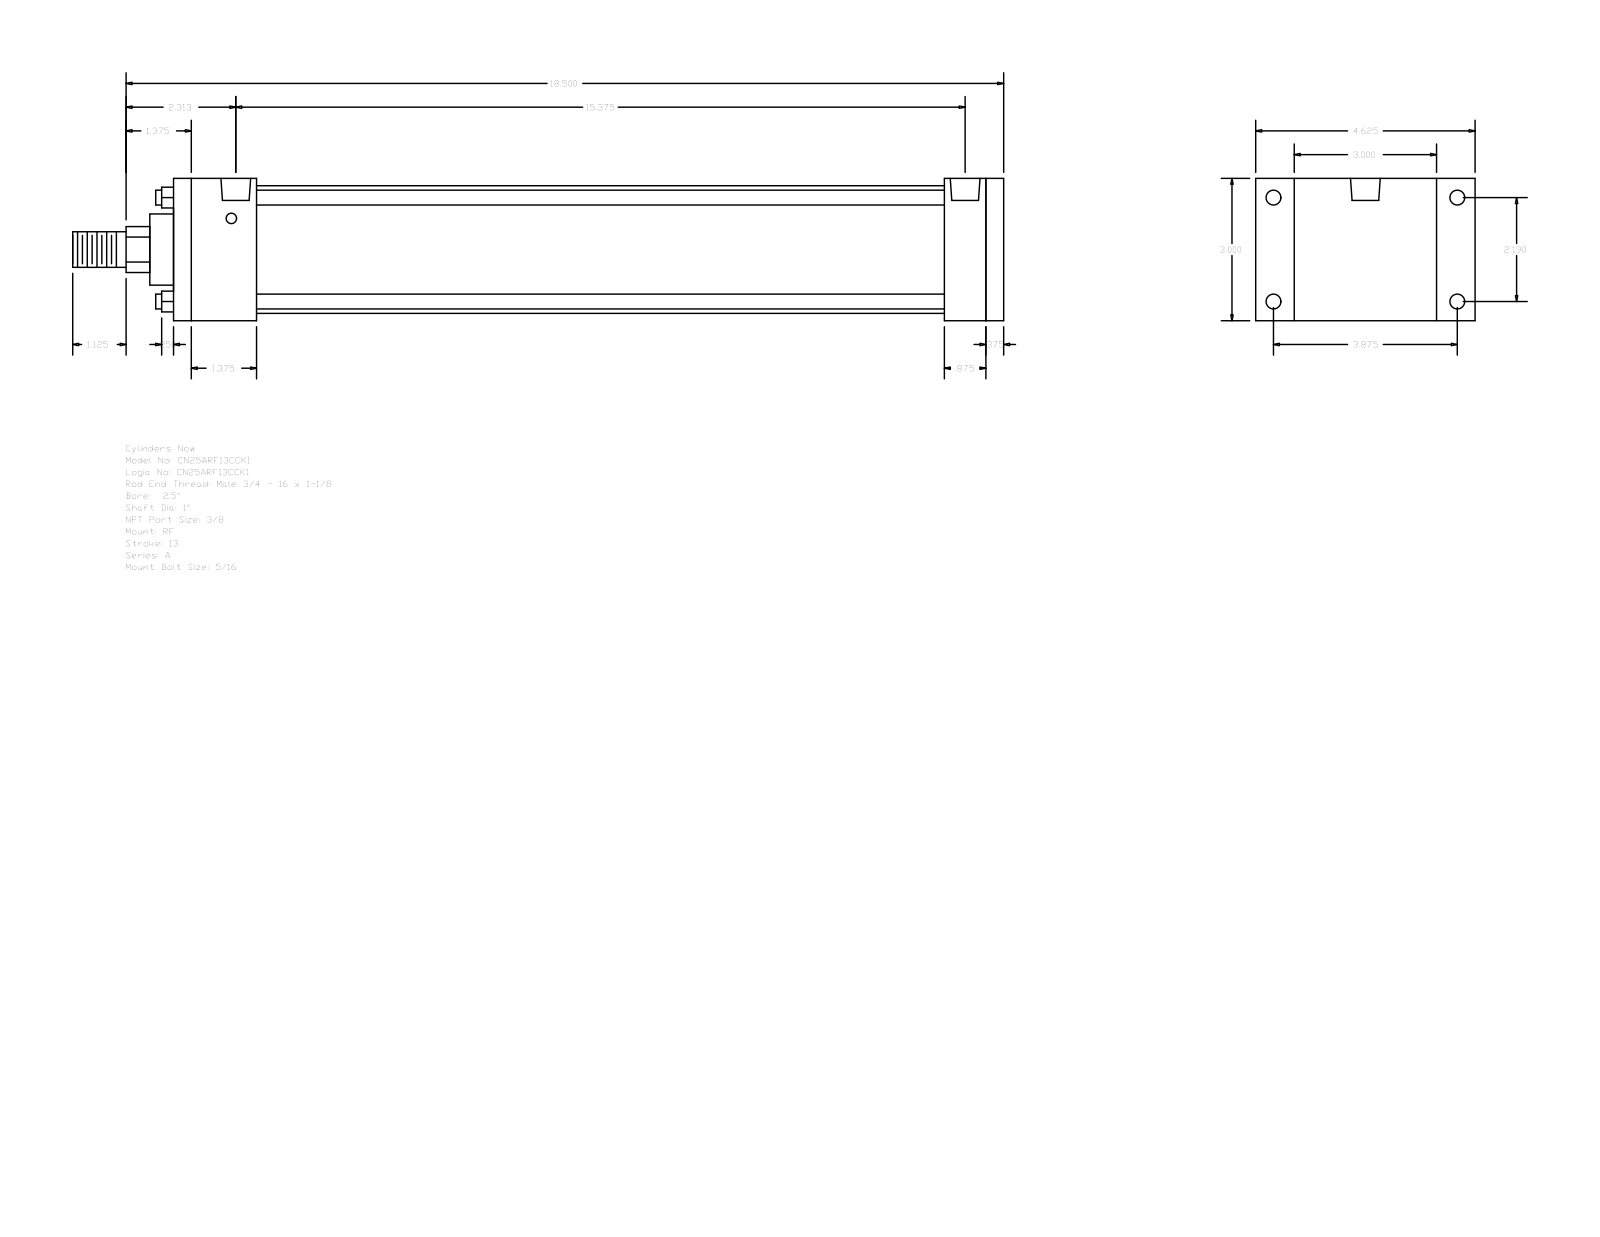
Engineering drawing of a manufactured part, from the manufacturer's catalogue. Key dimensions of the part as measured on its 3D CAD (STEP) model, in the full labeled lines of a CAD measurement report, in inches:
Part name (STEP PRODUCT): A_RF__0250_1
STEP written by: GSSL Pune (CONFIG_CONTROL_DESIGN)
Units: inches
Bodies: 0 solids, 92 faces (64 planar, 28 cylindrical, 0 other)
Overall size (bounding box): 19.625 × 4.625 × 3
Round holes (diameter × count): ⌀0.219 ×4, ⌀0.313 ×4, ⌀0.627 ×2
Round bosses / shafts (diameter × count): ⌀0.313 ×4, ⌀2.69 ×1, ⌀1.5 ×1, ⌀1 ×1, ⌀0.75 ×1
Partial cylindrical surfaces — rounded edges, fillets, slot ends (radius × count): R0.484 ×1
Main face-to-face distances: 3, 17.5, 0.375, 17.125, 1.75, 16.25, 14.5, 15.375, 15.75, 0.875
Hole centre spacings: 0.094, 2.19, 3.875, 4.451, 15.469, 15.562, 15.375
